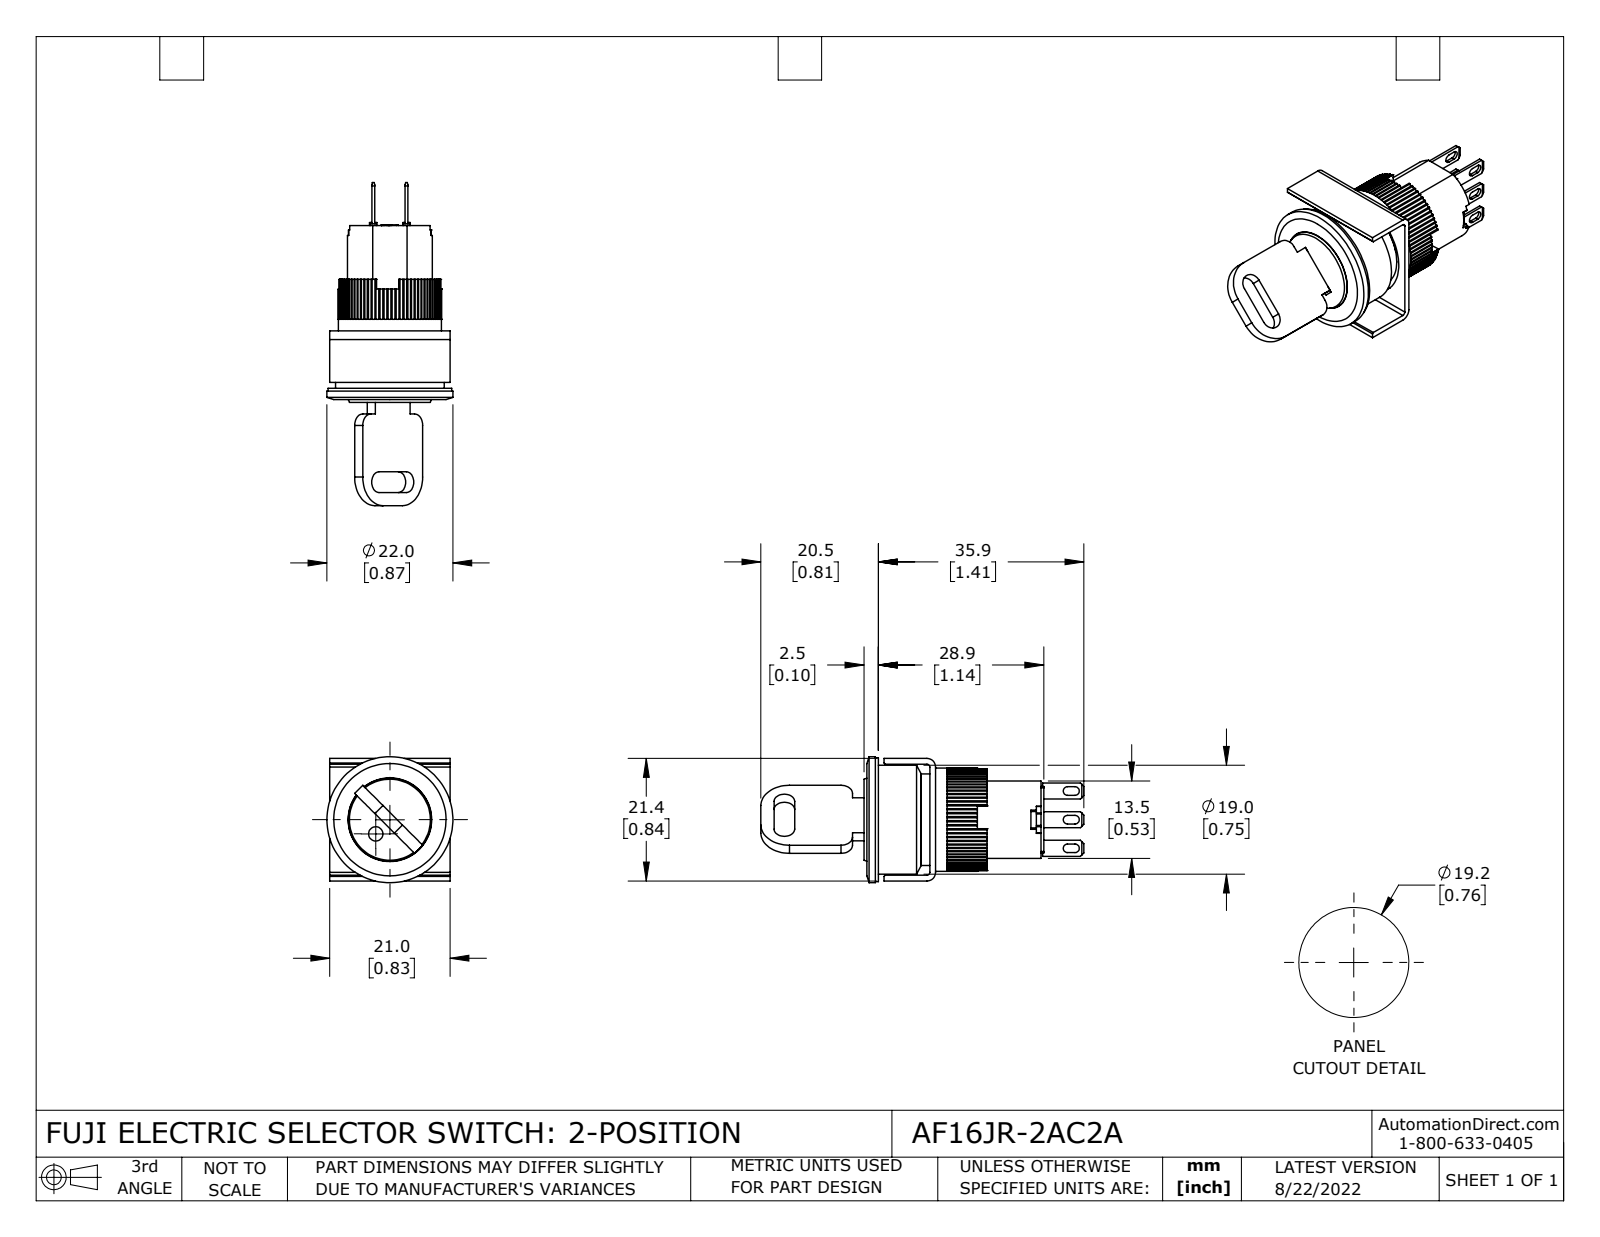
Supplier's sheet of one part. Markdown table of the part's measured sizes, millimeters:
| quantity | value |
| --- | --- |
| part name | AF16JR-2AC2A |
| STEP written by | SolidWorks 2021 (CONFIG_CONTROL_DESIGN) |
| units | millimeters |
| bodies | 13 solids, 707 faces (518 planar, 183 cylindrical, 6 other) |
| overall size | 56.4 × 22 × 22 |
| volume | 8 110 mm³ |
| surface area | 7 252 mm² |
| round holes (diameter × count) | 1 × 1, 2.5 × 1, 14.6 × 1, 18 × 1, 19 × 1 |
| round bosses / shafts (diameter × count) | 22 × 1, 21.6 × 1, 16 × 1, 14.8 × 1, 14.5 × 1 |
| partial cylindrical surfaces (radius × count) | 0.3 × 80, 0.2 × 12, 0.8 × 6, 0.5 × 2, 1.5 × 2, 1.8 × 2, 2 × 2, 5 × 2 |
| main face-to-face distances | 2, 1, 0.5, 9.5, 4.5, 10, 20.4, 2.5, 1.5, 19.4 |
| hole center spacings | 3.5 |
